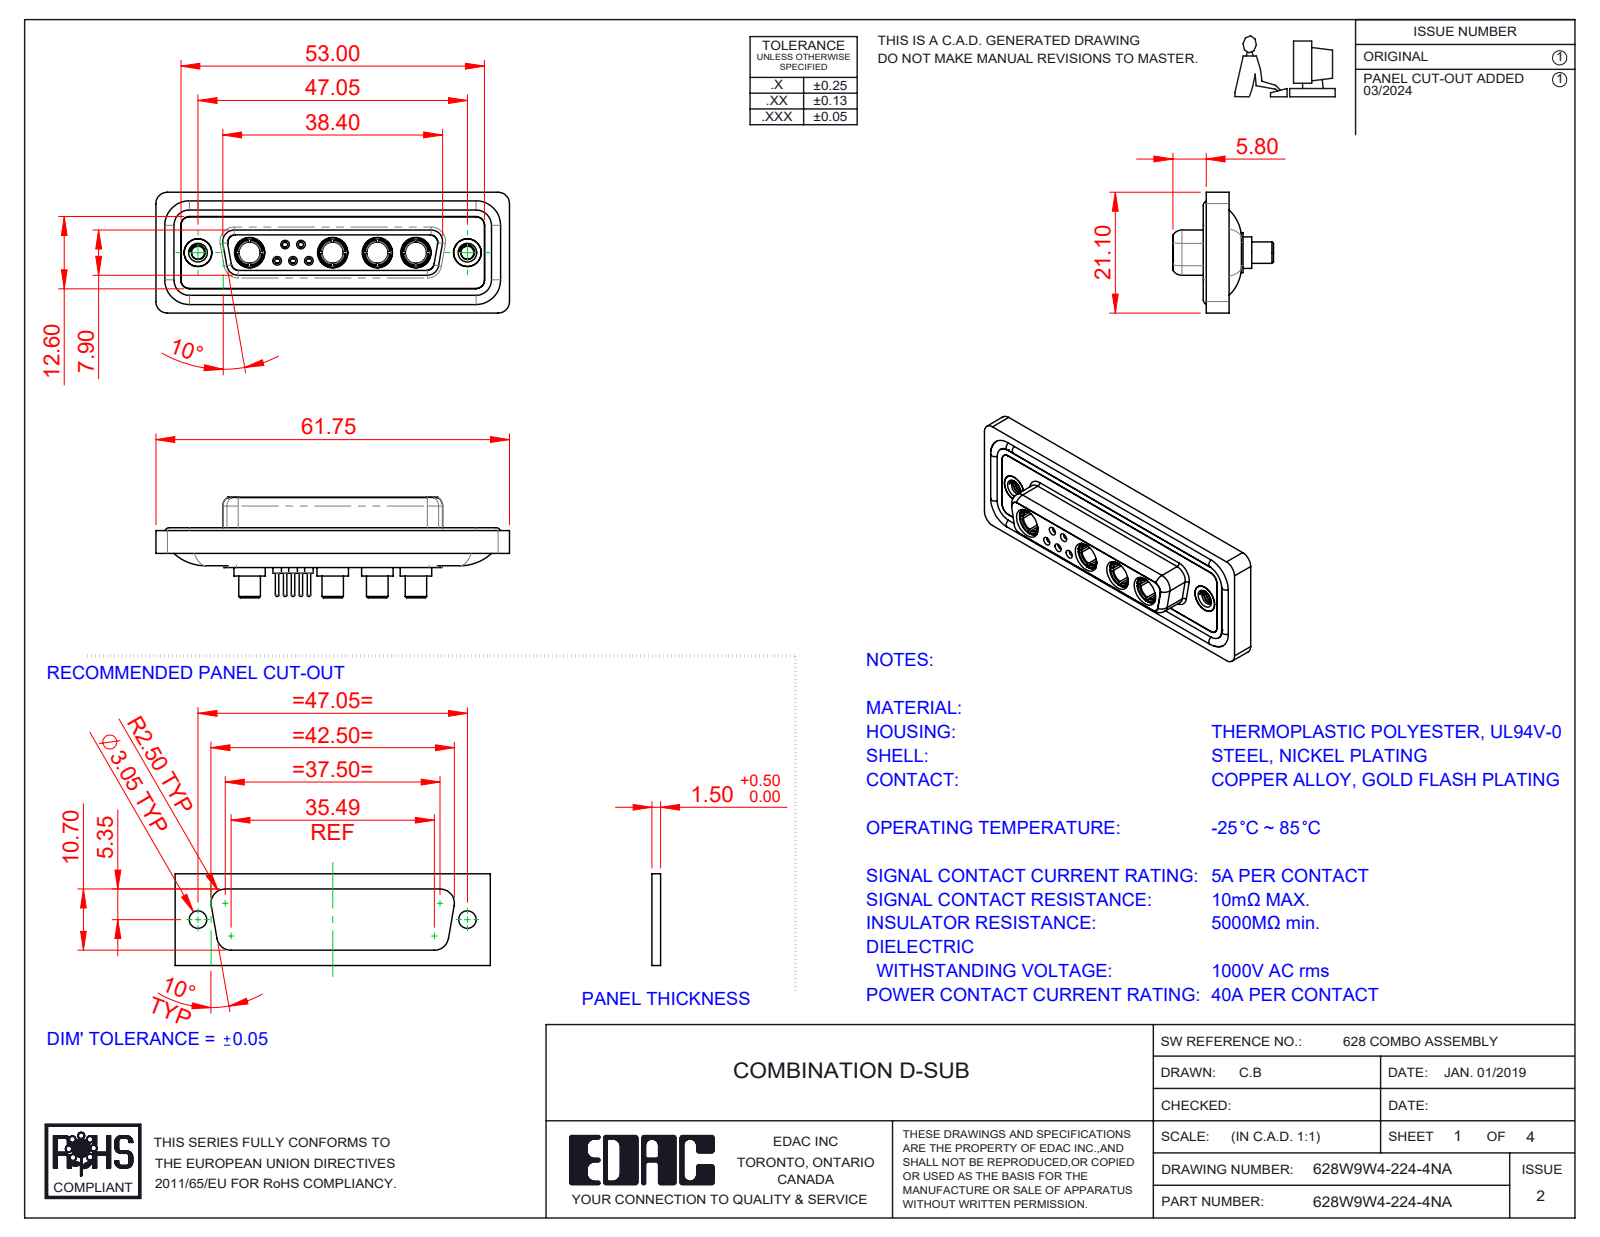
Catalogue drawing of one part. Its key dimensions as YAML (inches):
part_name: "628Combo Housing_9W4; 628Combo Threaded Rivet_A; Power Socket_40A S; 628Combo Shell Rear_25 Contacts (+5 more)"
step_written_by: "SolidWorks 2023 (CONFIG_CONTROL_DESIGN)"
units: inches
bodies: {solids: 20, faces: 955, planar: 296, cylindrical: 377, other: 282}
overall_size: [2.431, 0.831, 0.691]
volume: 0.506
surface_area: 21.08
round_holes:
  - {diameter: 0.191, count: 6}
  - {diameter: 0.035, count: 5}
  - {diameter: 0.043, count: 5}
  - {diameter: 0.059, count: 5}
  - {diameter: 0.079, count: 5}
  - {diameter: 0.146, count: 4}
  - {diameter: 0.209, count: 4}
  - {diameter: 0.063, count: 3}
  - {diameter: 0.067, count: 2}
  - {diameter: 0.089, count: 2}
  - {diameter: 0.157, count: 2}
  - {diameter: 0.159, count: 2}
round_bosses_or_shafts:
  - {diameter: 0.063, count: 6}
  - {diameter: 0.087, count: 5}
  - {diameter: 0.024, count: 5}
  - {diameter: 0.217, count: 4}
  - {diameter: 0.205, count: 4}
  - {diameter: 0.195, count: 4}
  - {diameter: 0.187, count: 4}
  - {diameter: 0.148, count: 4}
partial_cylinders:
  - {radius: 0.059, count: 22}
  - {radius: 0.079, count: 18}
  - {radius: 0.053, count: 8}
  - {radius: 0.063, count: 8}
  - {radius: 0.01, count: 4}
  - {radius: 0.02, count: 4}
  - {radius: 0.024, count: 4}
  - {radius: 0.026, count: 4}
face_to_face_distances: [0.016, 0.071, 0.293, 0.222, 0.02, 0.278, 0.26, 0.063, 0.043, 0.114]
hole_center_spacings: [0.124, 0.109, 0.198, 0.109, 0.173, 0.198, 0.218, 0.226]
